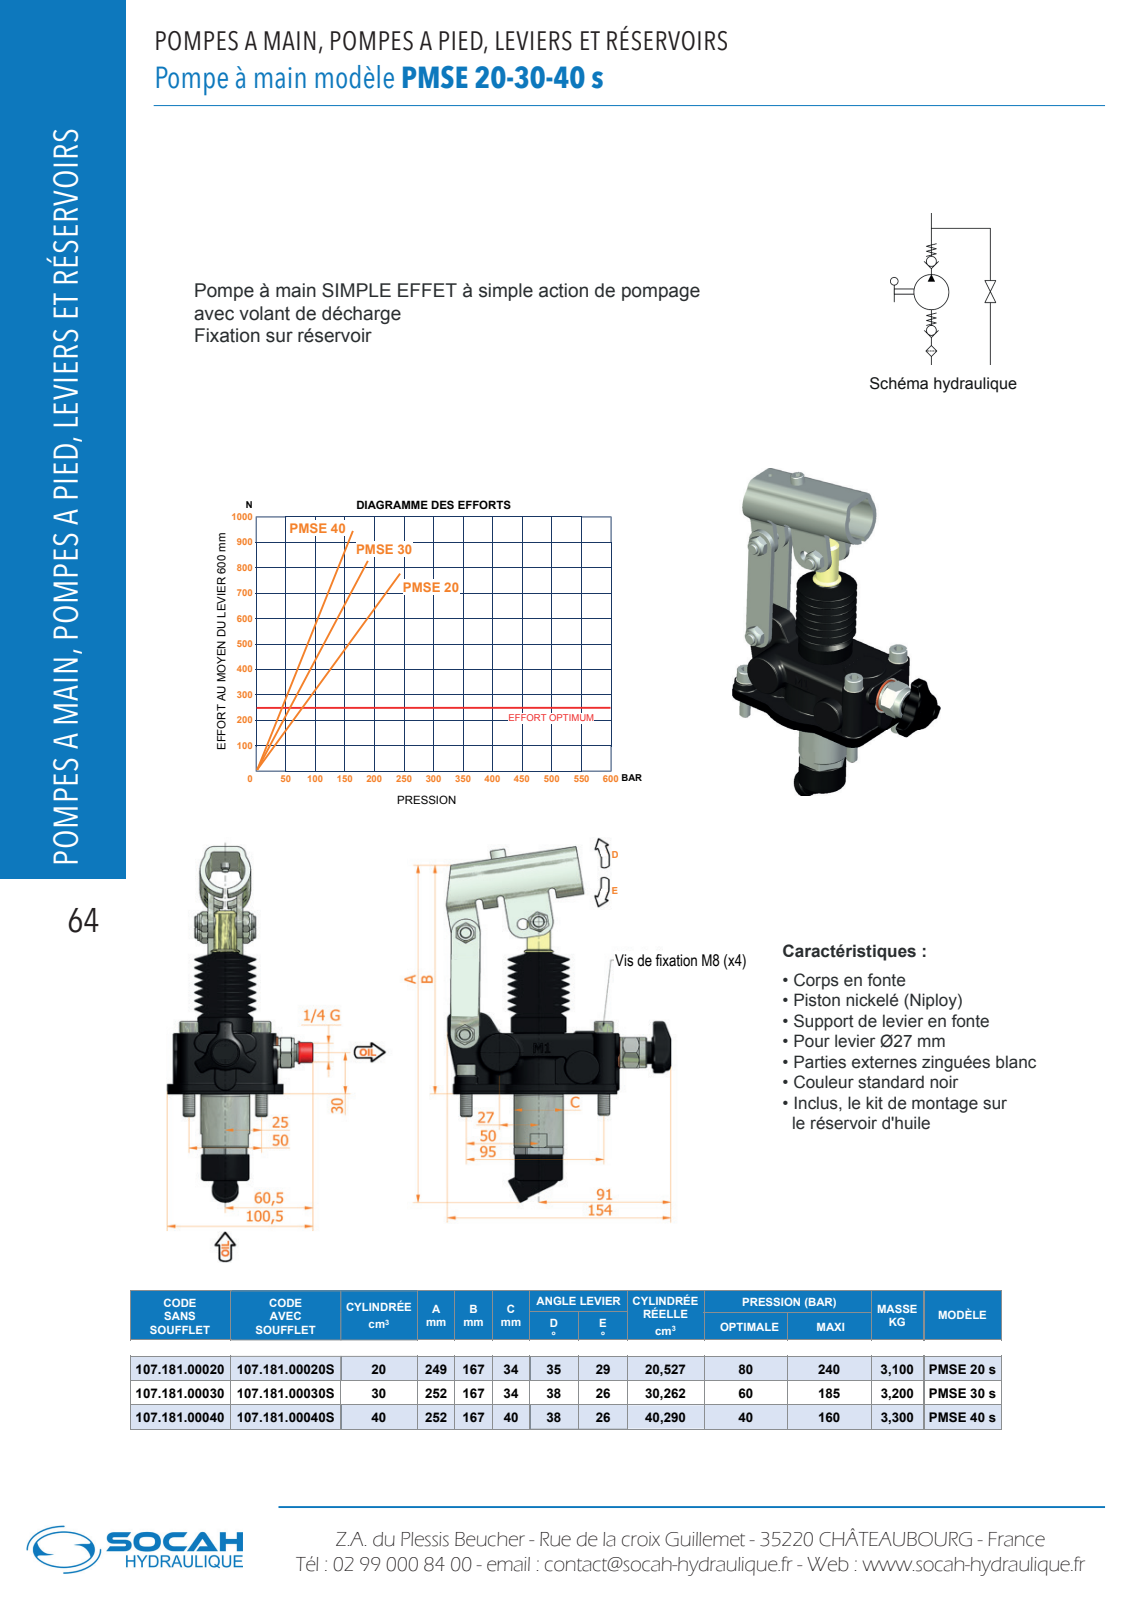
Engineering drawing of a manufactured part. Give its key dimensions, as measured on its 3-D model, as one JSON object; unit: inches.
{"part_name": "6067.0037.00", "step_written_by": "Autodesk Inventor 2013 (CONFIG_CONTROL_DESIGN)", "units": "inches", "bodies": {"solids": 1, "faces": 1566, "planar": 725, "cylindrical": 359, "other": 482}, "overall_size": [10.18, 6.099, 3.957], "volume_in3": 19.1, "surface_area_in2": 219.4, "round_holes": [[0.335, 4], [0.551, 4], [0.197, 2], [0.315, 2], [0.157, 1], [0.709, 1], [0.748, 1], [0.807, 1], [0.866, 1], [1.142, 1]], "round_bosses_or_shafts": [[0.315, 7], [0.512, 4], [0.472, 4], [0.435, 3], [0.906, 2], [0.787, 2], [0.63, 2], [0.394, 2]], "partial_cylinders_radius": [[0.039, 36], [0.008, 24], [0.079, 20], [0.004, 16], [0.197, 15], [0.394, 10], [0.118, 9], [0.315, 9]], "face_to_face_distances": [0.079, 0.157, 0.276, 1.378, 1.654, 0.787, 0.63, 1.457, 1.732, 0.197], "hole_center_spacings": [1.028, 1.969, 2.027, 2.201, 3.583, 3.74, 4.226, 1.476]}
